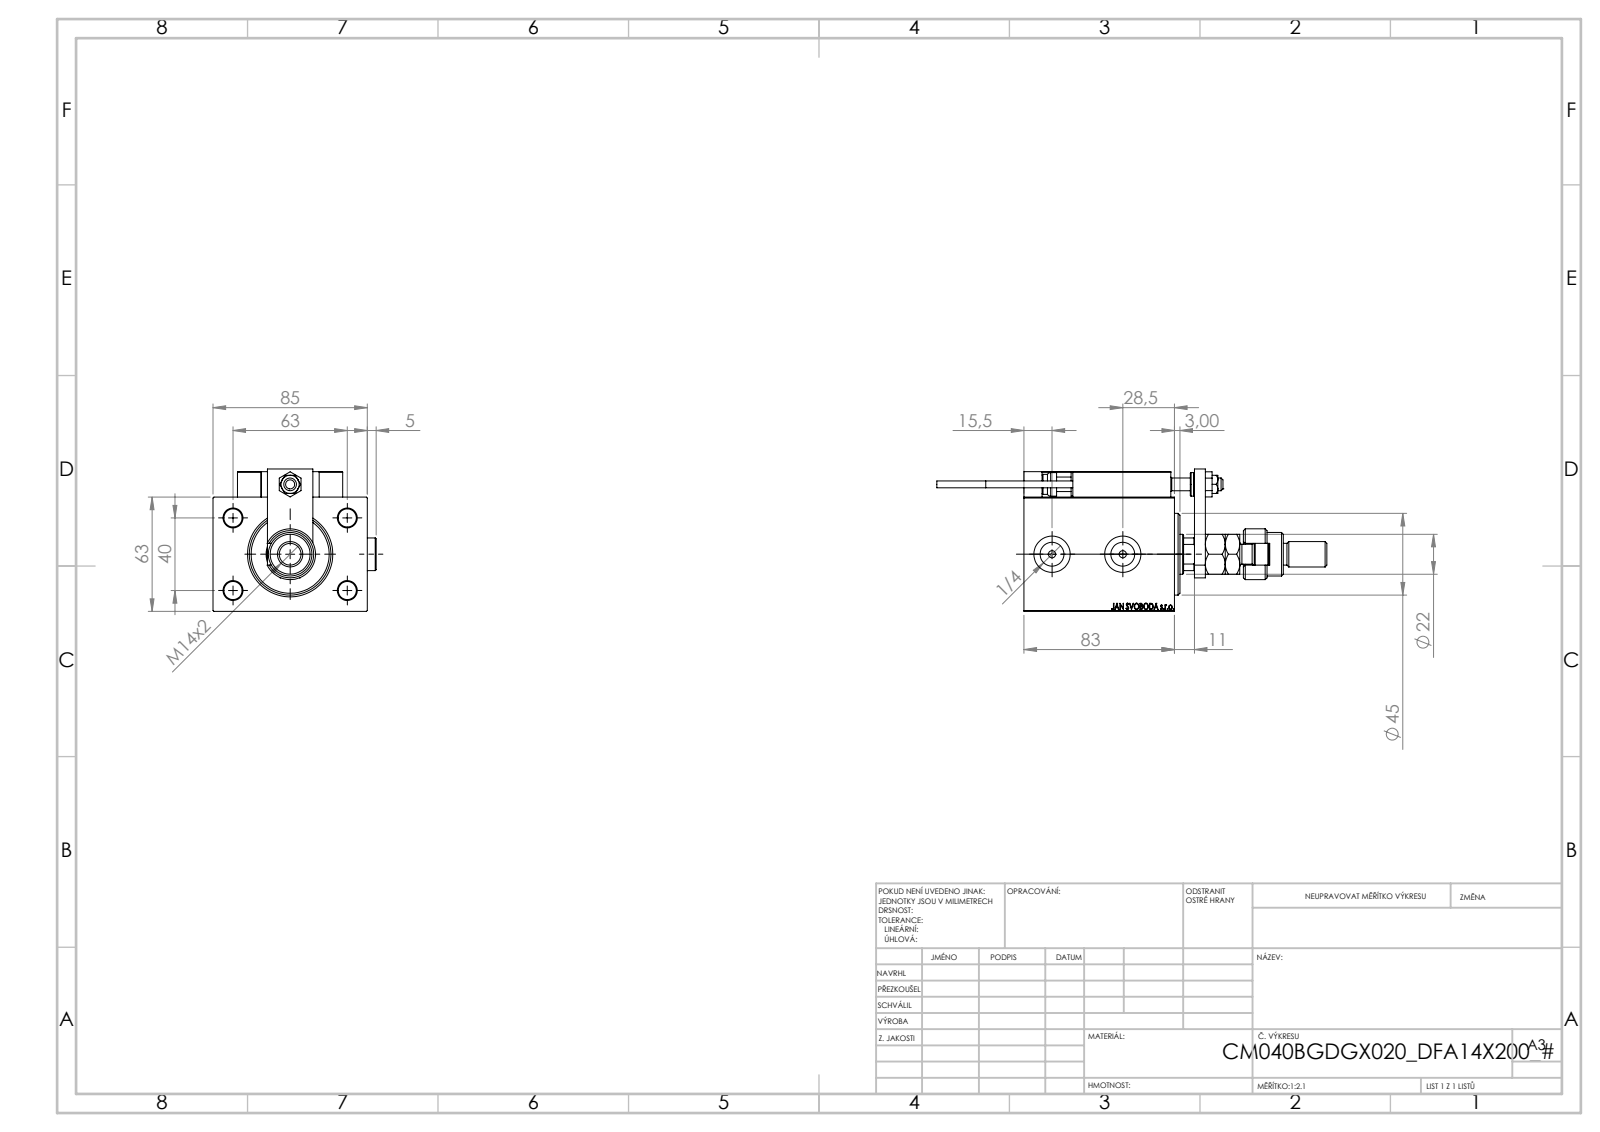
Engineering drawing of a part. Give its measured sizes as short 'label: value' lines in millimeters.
name: TYC_L79; X_Y_DFA; ALLEN BOLT D8; V450CM_B_VCP (+7 more)
written by: SolidWorks 2019 (CONFIG_CONTROL_DESIGN)
unit: mm
bodies: 28 solids, 1455 faces (623 planar, 211 cylindrical, 621 other)
size: 215 × 89.9 × 78.5
volume: 491 571 mm³; area: 100 383 mm²
holes: 6× ⌀4, 5× ⌀8, 4× ⌀3.2, 4× ⌀10, 2× ⌀5, 2× ⌀13.16, 2× ⌀20, 1× ⌀7, 1× ⌀12.5, 1× ⌀16.5, 1× ⌀22, 1× ⌀25.5
bosses: 3× ⌀18, 2× ⌀11, 2× ⌀5, 2× ⌀3.8, 1× ⌀28, 1× ⌀24, 1× ⌀14, 1× ⌀13
rounds: 30× R0.3, 2× R3, 1× R9.75, 1× R10.5
face distances: 63, 85, 14, 32, 83, 51, 17, 51.4, 10, 77
hole spacings: 37.31, 11.37, 20, 29.59, 29.69, 35.06, 36.06, 36.53
